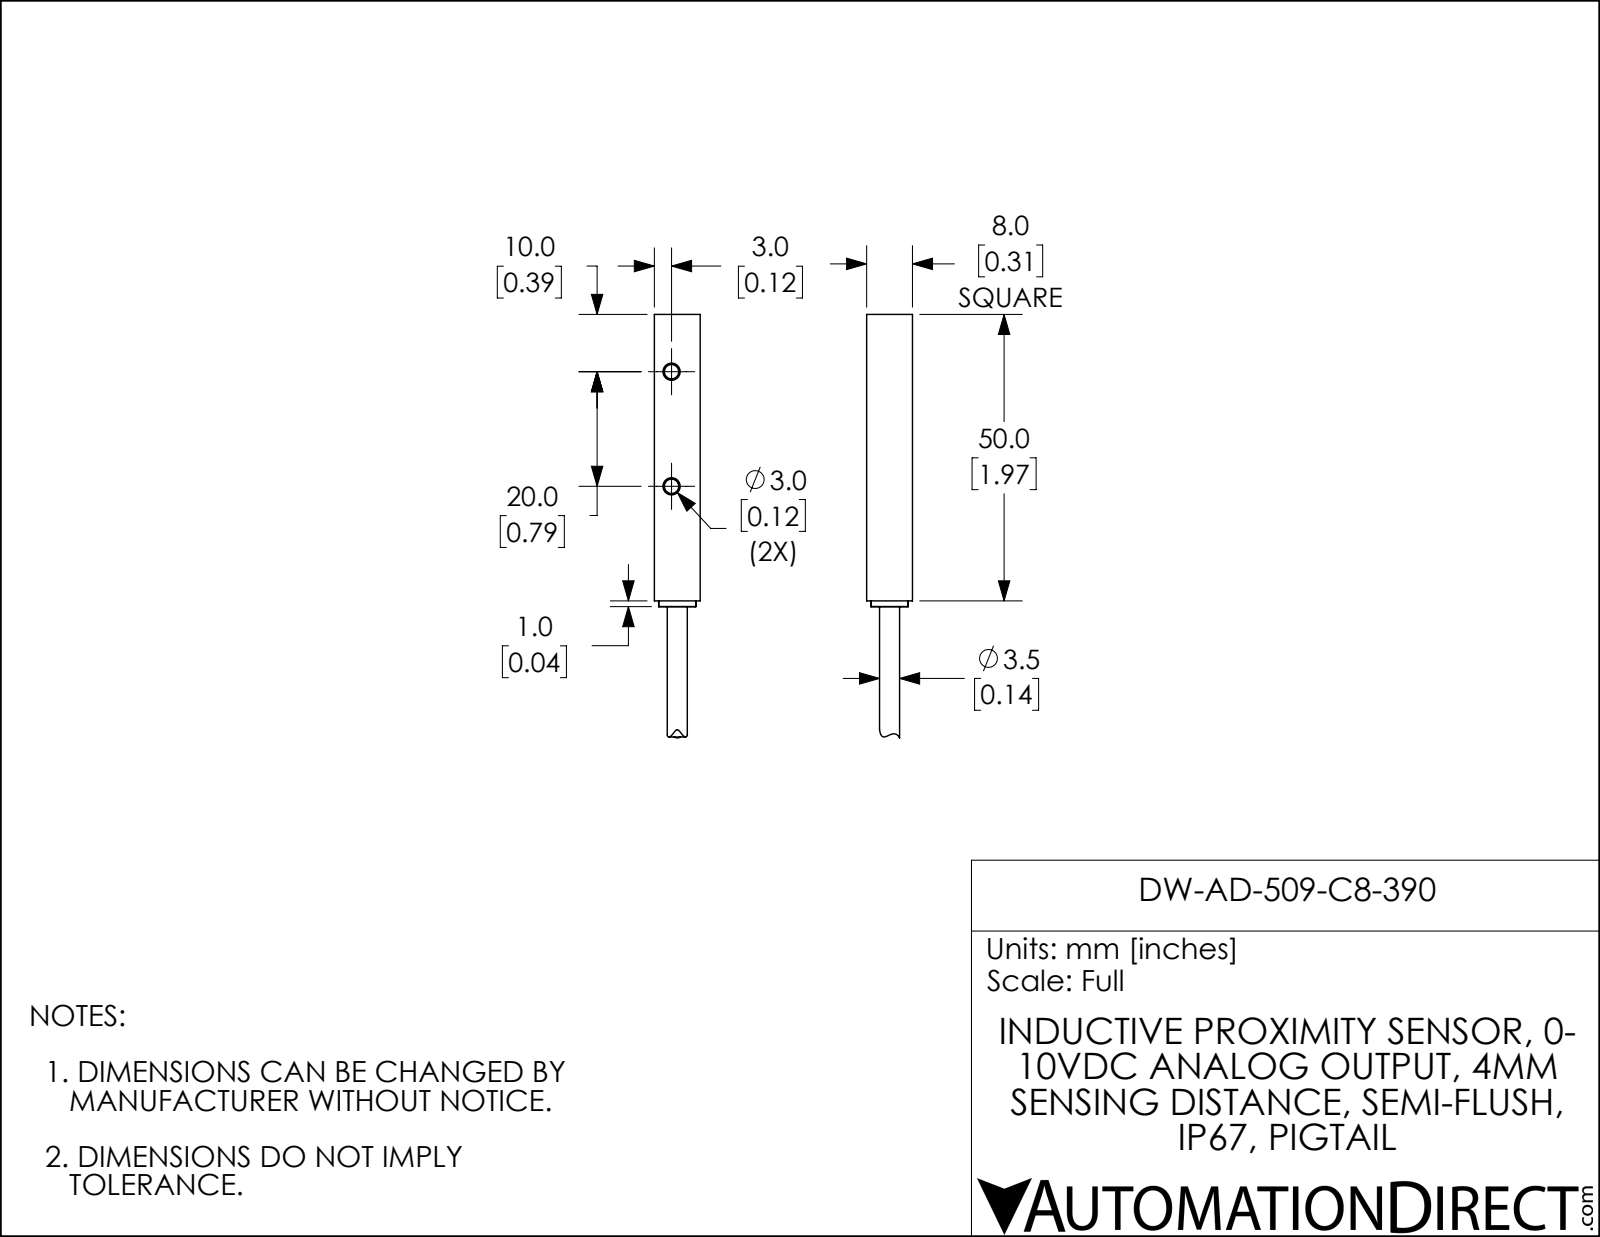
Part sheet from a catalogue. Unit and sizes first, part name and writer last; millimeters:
Units: millimetres
Overall size (bounding box): 73.9 × 8 × 8
Round holes (diameter × count): ⌀2.5 ×2, ⌀3.5 ×1
Round bosses / shafts (diameter × count): ⌀6.5 ×1
Main face-to-face distances: 8, 50, 1, 51, 5, 4, 46
Hole centre spacings: 20
Volume: 3 420 mm³ · Surface area: 2 310 mm²
Bodies: 4 solids, 25 faces (12 planar, 7 cylindrical, 6 other)
Part name (STEP PRODUCT): DW-AD-509-C8-39x
STEP written by: SolidWorks 2018 (AUTOMOTIVE_DESIGN)
